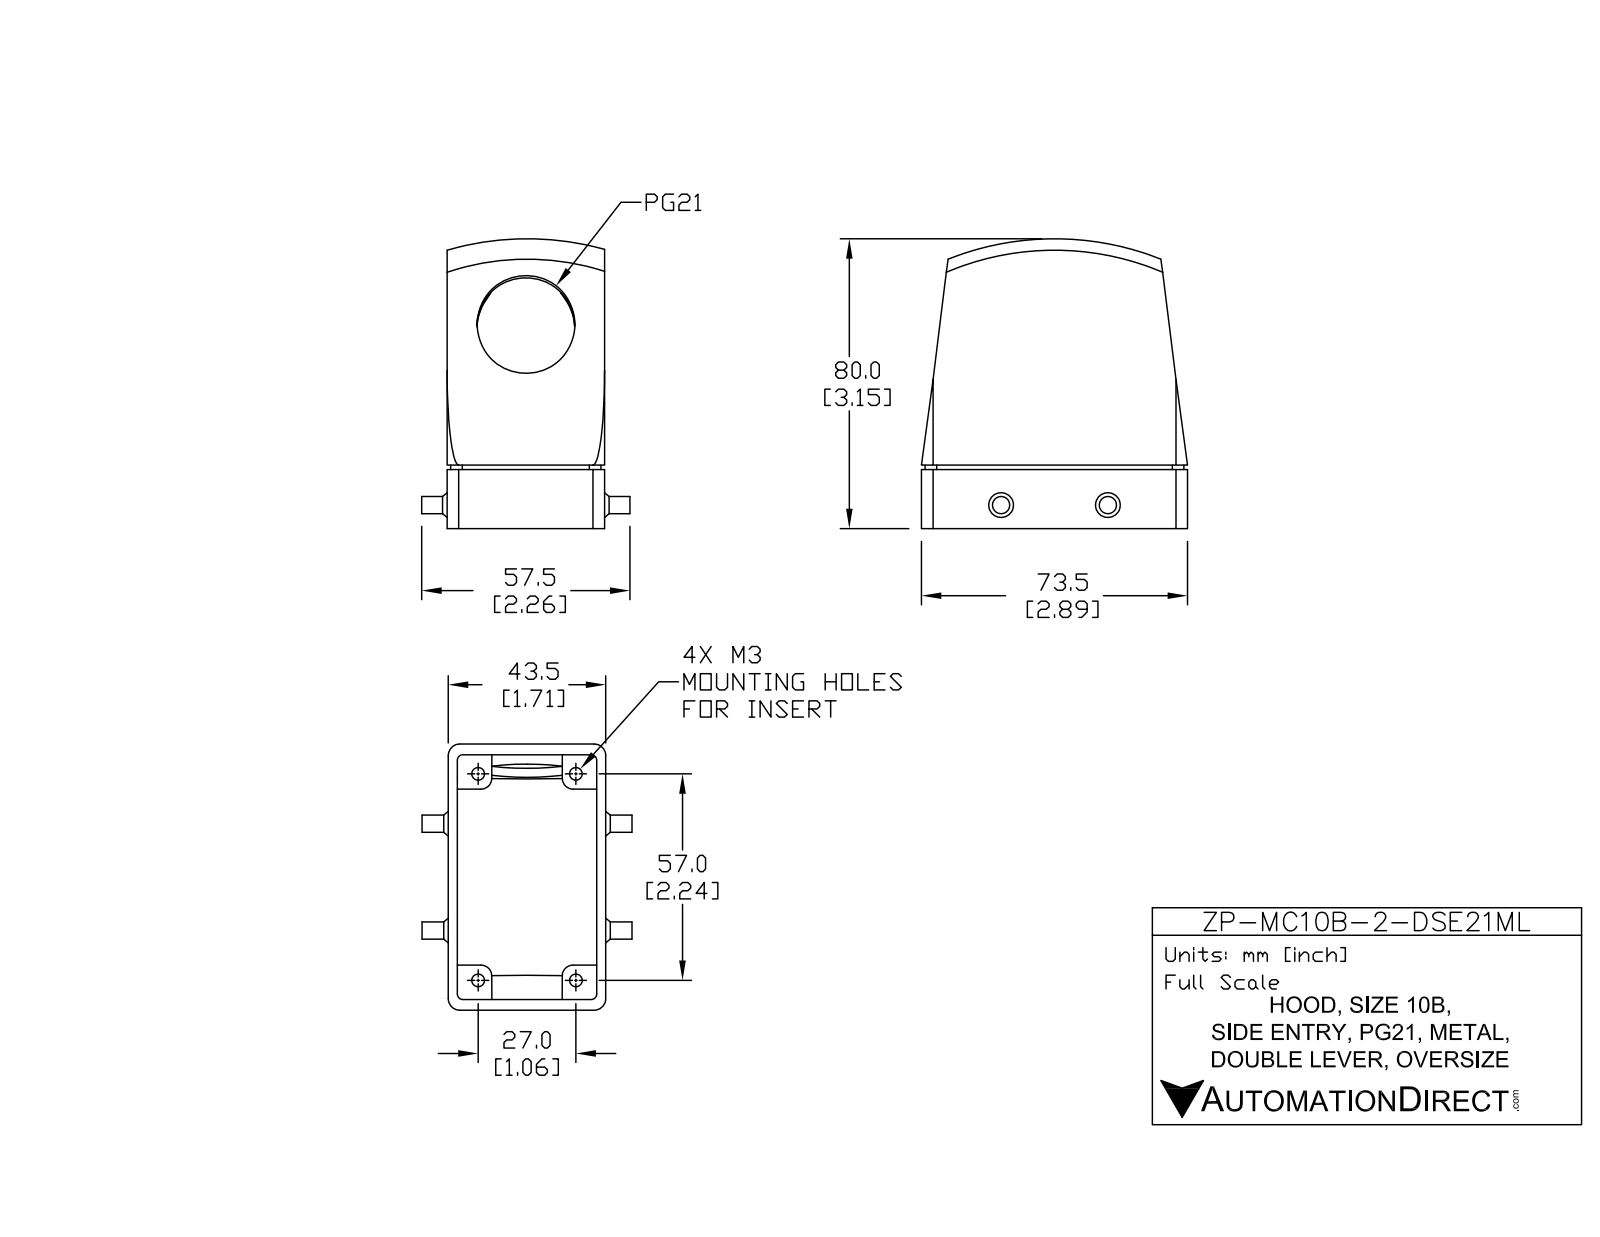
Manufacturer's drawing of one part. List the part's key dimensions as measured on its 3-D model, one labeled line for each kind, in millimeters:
Part name (STEP PRODUCT): ZP-MC10B-2-DSE21ML
STEP written by: SolidWorks 2011 (AUTOMOTIVE_DESIGN)
Units: millimetres
Bodies: 5 solids, 100 faces (56 planar, 34 cylindrical, 10 other)
Overall size (bounding box): 77.55 × 73.5 × 58
Volume: 57 665 mm³ · Surface area: 43 843 mm²
Round holes (diameter × count): ⌀3.5 ×4, ⌀27 ×1
Round bosses / shafts (diameter × count): ⌀4.75 ×2
Partial cylindrical surfaces — rounded edges, fillets, slot ends (radius × count): R3.2 ×8, R0.7 ×4, R3 ×4
Main face-to-face distances: 2.5, 41, 43.5, 38.5, 9.5, 58.08, 2.96, 12.46, 61.04, 70.54
Hole centre spacings: 28.96, 59, 65.72
